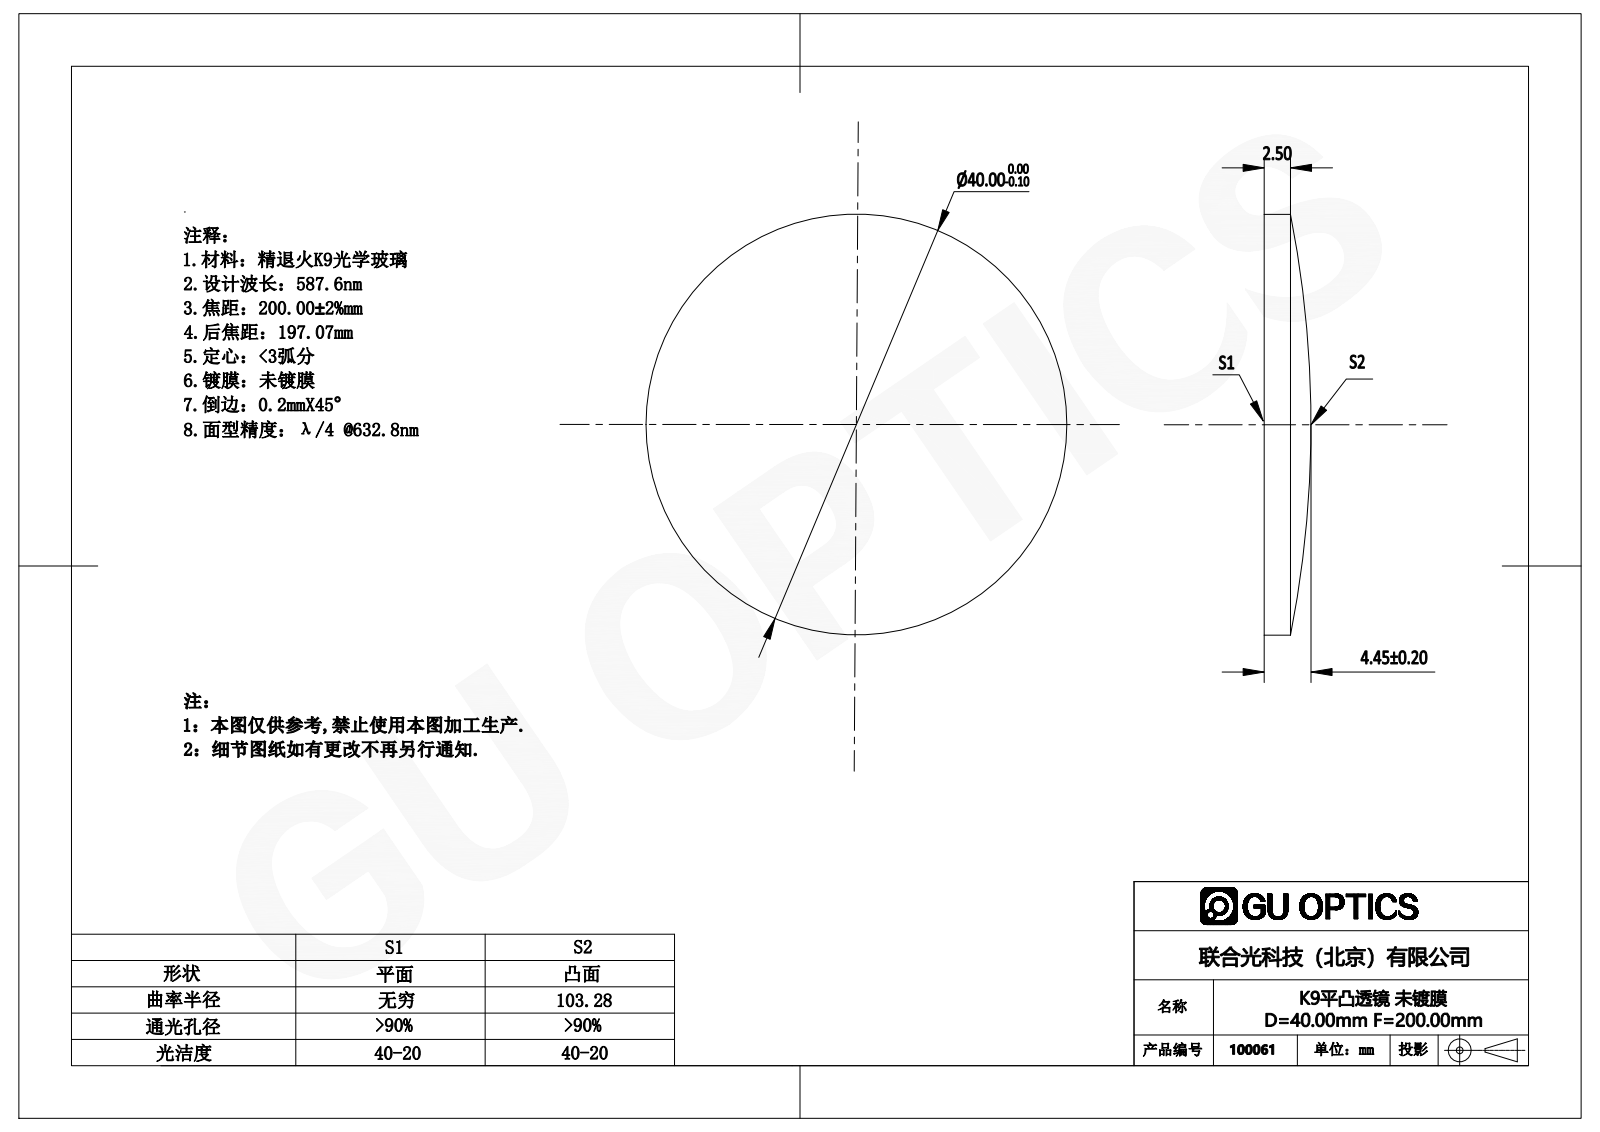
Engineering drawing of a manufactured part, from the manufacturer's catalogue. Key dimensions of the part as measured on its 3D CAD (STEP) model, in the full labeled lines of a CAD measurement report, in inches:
Part name (STEP PRODUCT): 100061
STEP written by: SolidWorks 2016 (AUTOMOTIVE_DESIGN)
Units: inches
Bodies: 1 solid, 5 faces (1 planar, 2 cylindrical, 2 other)
Overall size (bounding box): 1.575 × 1.575 × 0.175
Volume: 0.267 in³ · Surface area: 4.4 in²
Round bosses / shafts (diameter × count): ⌀1.575 ×1
